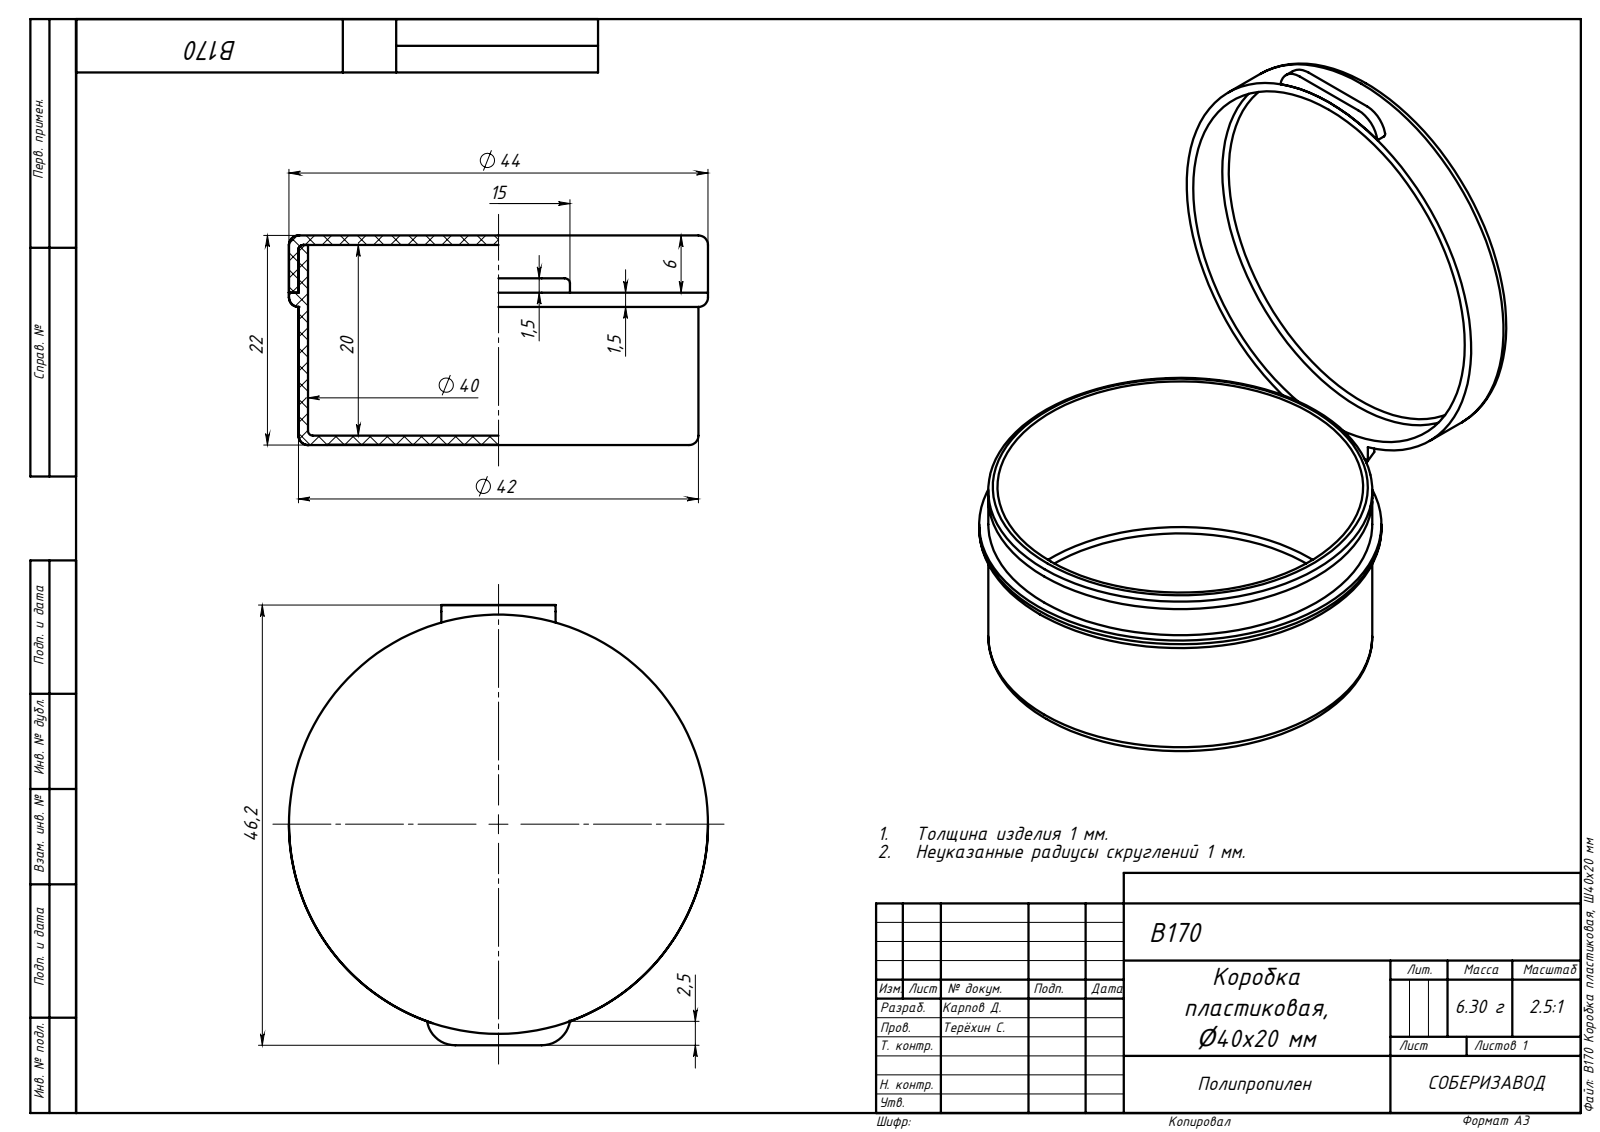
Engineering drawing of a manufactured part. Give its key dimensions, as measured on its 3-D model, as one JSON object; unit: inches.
{"part_name": "B170 Емкость; B170 Крышка; B170 Коробка пластиковая, O40x20 мм", "step_written_by": "SolidWorks 2020 (AUTOMOTIVE_DESIGN)", "units": "inches", "bodies": {"solids": 3, "faces": 53, "planar": 20, "cylindrical": 19, "other": 14}, "overall_size": [1.819, 1.732, 0.866], "volume_in3": 0.38, "surface_area_in2": 19.78, "round_holes": [[1.417, 1], [1.575, 1]], "round_bosses_or_shafts": [[1.732, 1], [1.654, 1], [1.654, 1]], "partial_cylinders_radius": [[0.118, 2], [0.02, 1]], "face_to_face_distances": [0.039, 0.827, 0.787, 0.035, 0.823, 0.862, 0.197, 0.591, 0.236, 0.626]}
